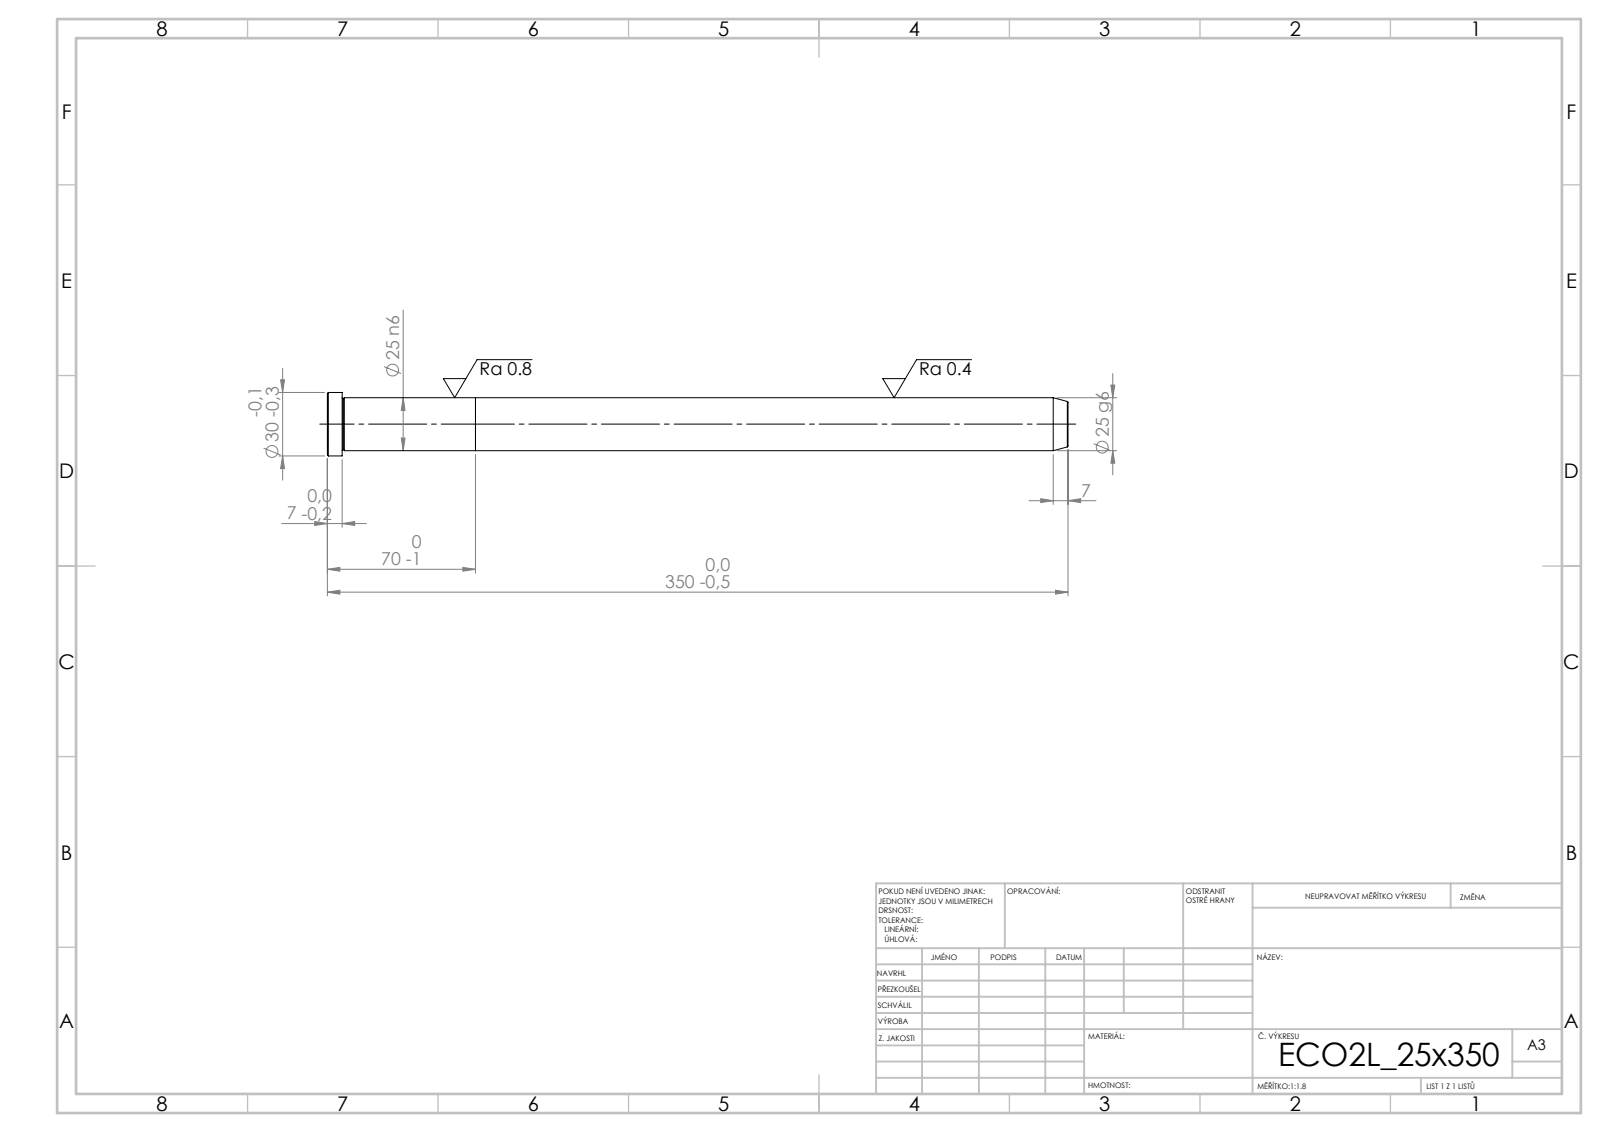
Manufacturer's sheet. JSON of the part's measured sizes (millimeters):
{"step_written_by": "SolidWorks 2019 (CONFIG_CONTROL_DESIGN)", "units": "millimeters", "bodies": {"solids": 2, "faces": 21, "planar": 5, "cylindrical": 6, "other": 10}, "overall_size": [350, 30, 30], "volume_mm3": 172784, "surface_area_mm2": 29841, "round_bosses_or_shafts": [[30, 1], [25, 1]], "face_to_face_distances": [70, 280, 350, 343, 63, 7]}
